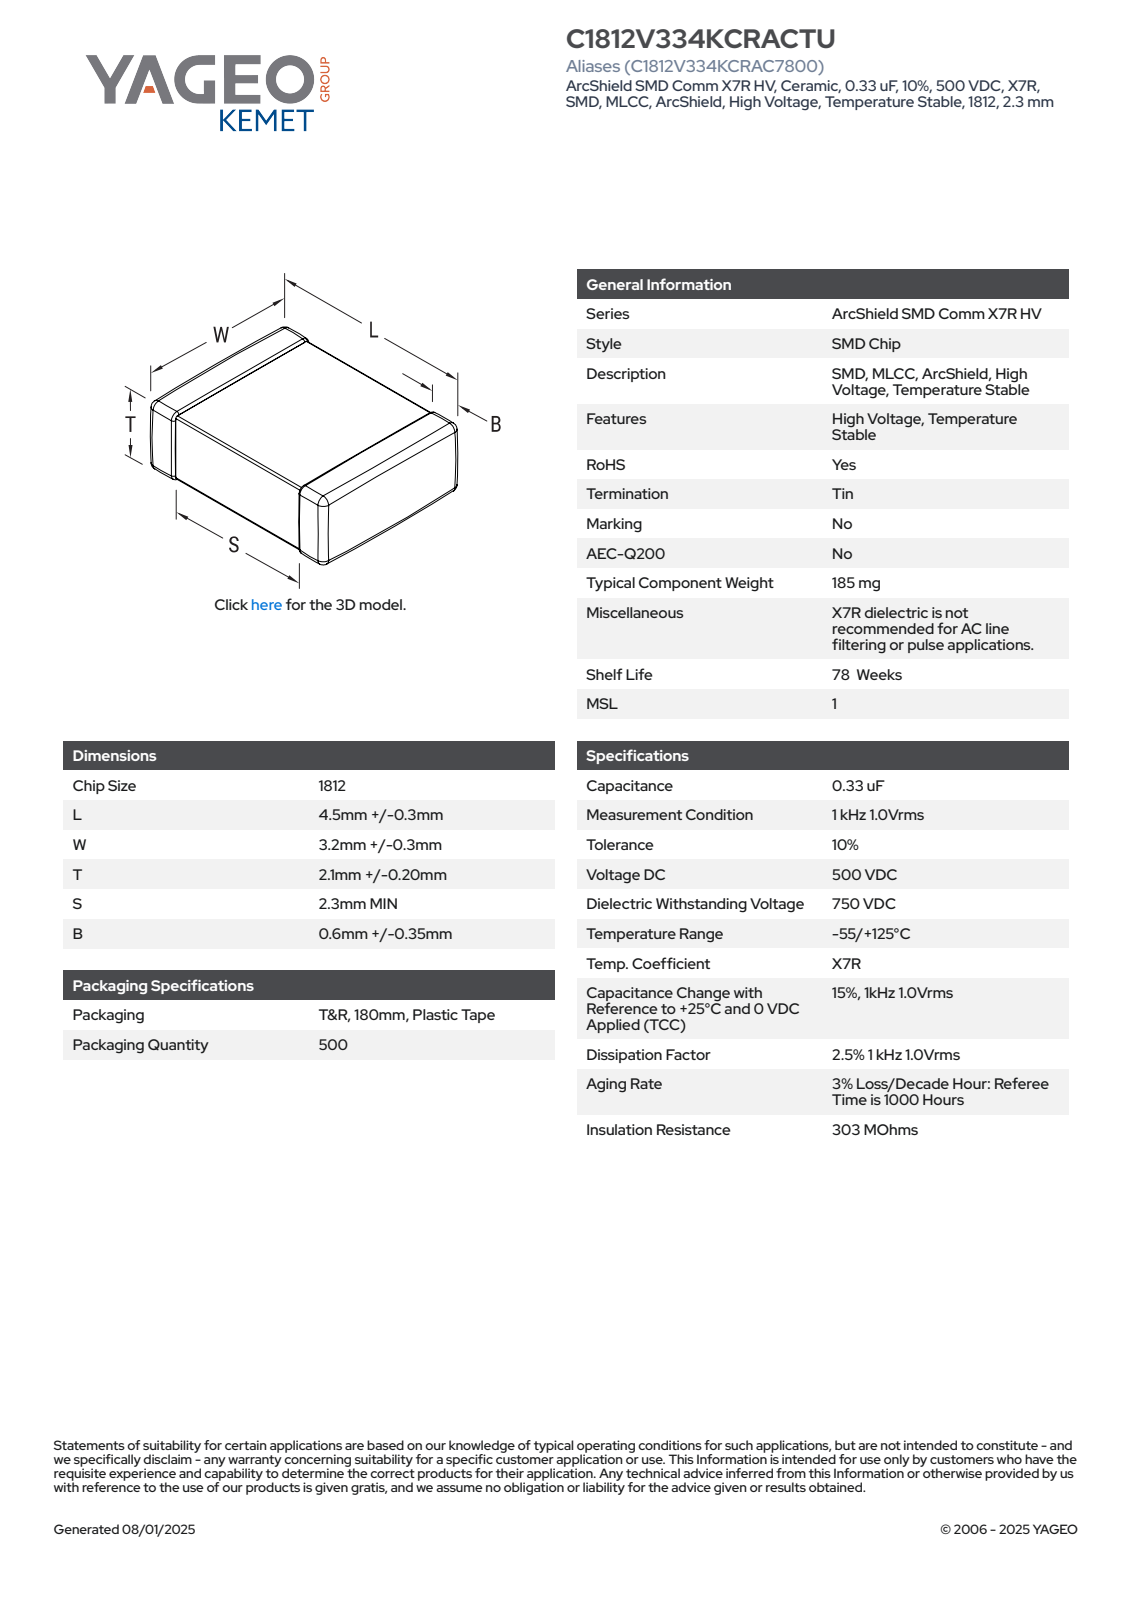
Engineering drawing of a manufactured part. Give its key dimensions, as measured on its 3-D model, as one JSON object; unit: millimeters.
{"part_name": "CCS_CCSTD_1812_L4.8W3.5T2.3B0.6", "step_written_by": "SolidWorks 2021 (AUTOMOTIVE_DESIGN)", "units": "millimeters", "bodies": {"solids": 4, "faces": 129, "planar": 71, "cylindrical": 42, "other": 16}, "overall_size": [4.8, 3.5, 2.3], "volume_mm3": 36, "surface_area_mm2": 71, "face_to_face_distances": [2.23, 2.16, 4.8, 3.43, 3.36, 2.3, 3.5, 2.08, 2.72, 2.59]}
